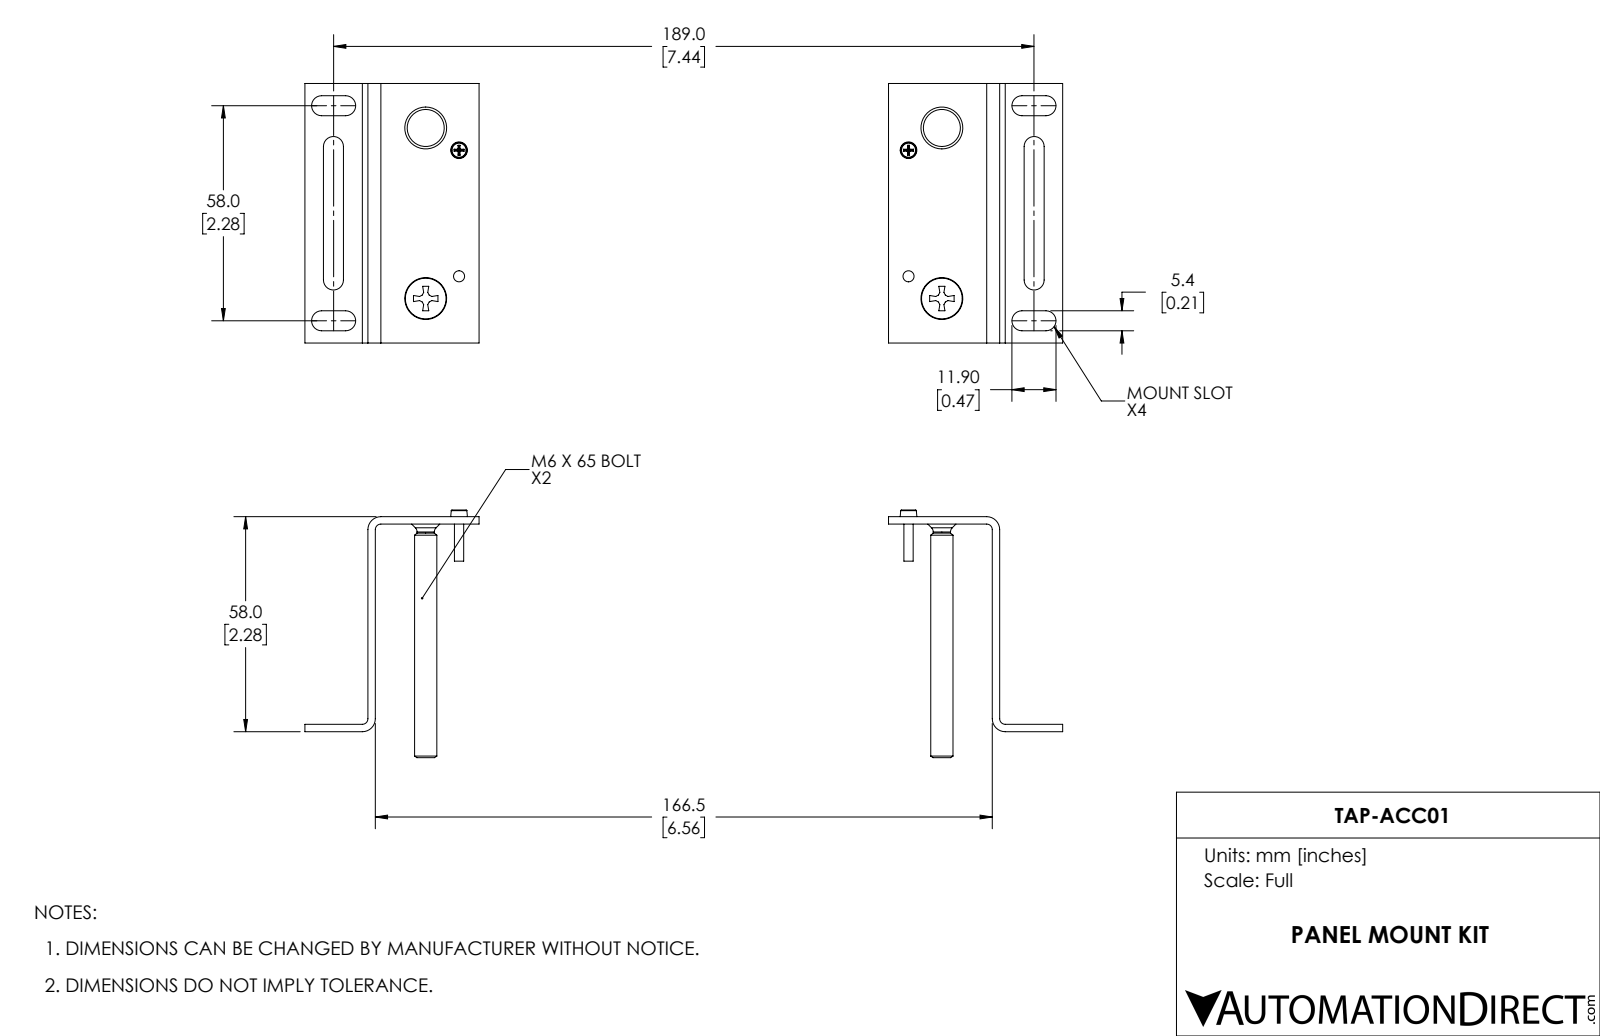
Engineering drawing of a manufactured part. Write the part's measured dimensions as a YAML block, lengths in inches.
part_name: "TAP-ACC01"
step_written_by: "SolidWorks 2017 (AUTOMOTIVE_DESIGN)"
units: inches
bodies: {solids: 6, faces: 230, planar: 110, cylindrical: 70, other: 50}
overall_size: [8.051, 2.756, 2.63]
volume: 1.483
surface_area: 40.92
round_holes:
  - {diameter: 0.118, count: 4}
  - {diameter: 0.394, count: 4}
  - {diameter: 0.445, count: 4}
  - {diameter: 1.693, count: 1}
round_bosses_or_shafts:
  - {diameter: 0.433, count: 2}
  - {diameter: 0.236, count: 2}
  - {diameter: 0.184, count: 2}
  - {diameter: 0.098, count: 2}
  - {diameter: 0.088, count: 2}
partial_cylinders:
  - {radius: 0.106, count: 12}
  - {radius: 0.059, count: 4}
  - {radius: 0.138, count: 4}
face_to_face_distances: [0.079, 6.634, 2.205, 6.555, 6.713, 2.283, 2.126, 2.756, 1.181, 5.531]
hole_center_spacings: [0.426, 1.614, 5.135, 5.366, 1.339, 1.811, 4.776, 4.959]
